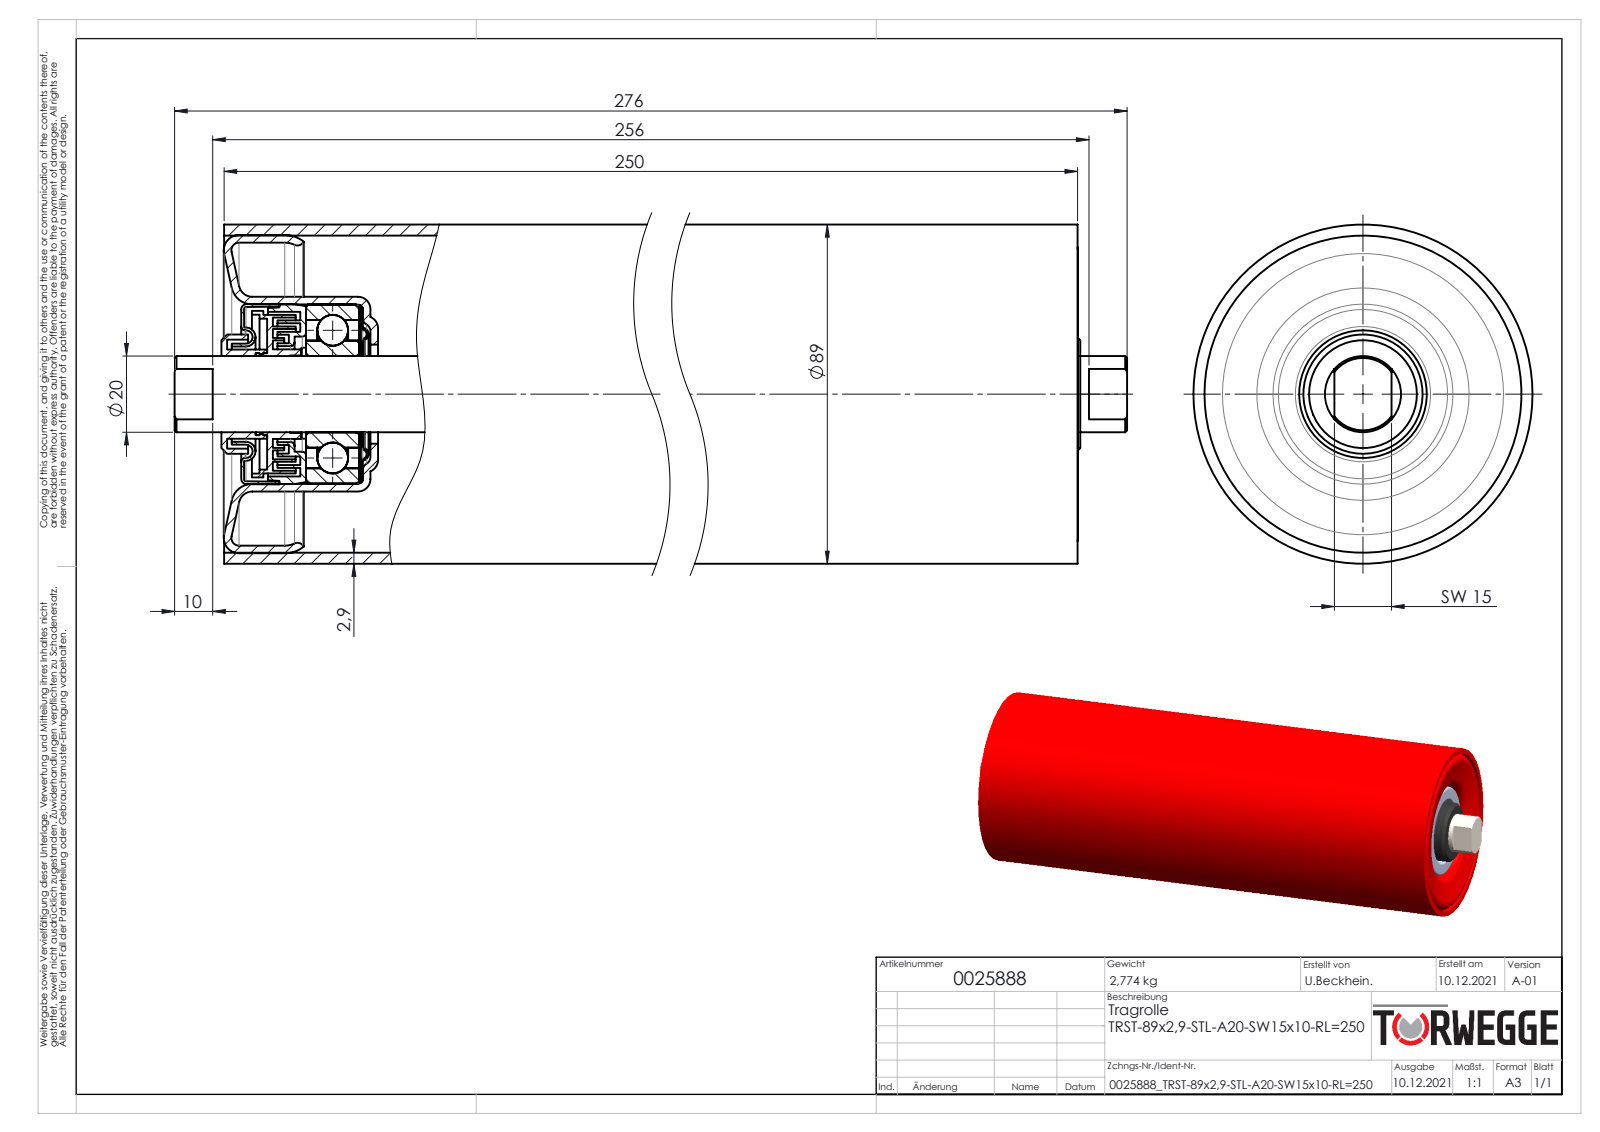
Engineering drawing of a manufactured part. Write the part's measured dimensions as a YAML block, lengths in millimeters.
part_name: "0025888"
step_written_by: "SolidWorks 2020 (AUTOMOTIVE_DESIGN)"
units: millimeters
bodies: {solids: 24, faces: 606, planar: 114, cylindrical: 244, other: 248}
overall_size: [276, 89, 89]
volume: 434650
surface_area: 309529
round_holes:
  - {diameter: 2, count: 4}
  - {diameter: 19, count: 1}
  - {diameter: 19.6, count: 1}
  - {diameter: 20, count: 1}
  - {diameter: 20.3, count: 1}
  - {diameter: 21, count: 1}
  - {diameter: 21.5, count: 1}
  - {diameter: 25, count: 1}
  - {diameter: 25.2, count: 1}
  - {diameter: 26, count: 1}
  - {diameter: 28.2, count: 1}
  - {diameter: 28.6, count: 1}
round_bosses_or_shafts:
  - {diameter: 23.9, count: 2}
  - {diameter: 89, count: 1}
  - {diameter: 83.5, count: 1}
  - {diameter: 51.1, count: 1}
  - {diameter: 47.2, count: 1}
  - {diameter: 47, count: 1}
  - {diameter: 46.5, count: 1}
  - {diameter: 43.7, count: 1}
partial_cylinders:
  - {radius: 2, count: 8}
  - {radius: 13.5, count: 1}
face_to_face_distances: [14, 193.02, 14.92, 192.1, 0.92, 178.1, 207.02, 10.2, 24.2, 25.12]
hole_center_spacings: [11.49, 11.5, 22.55, 3.99, 4, 21.43, 22.99]
